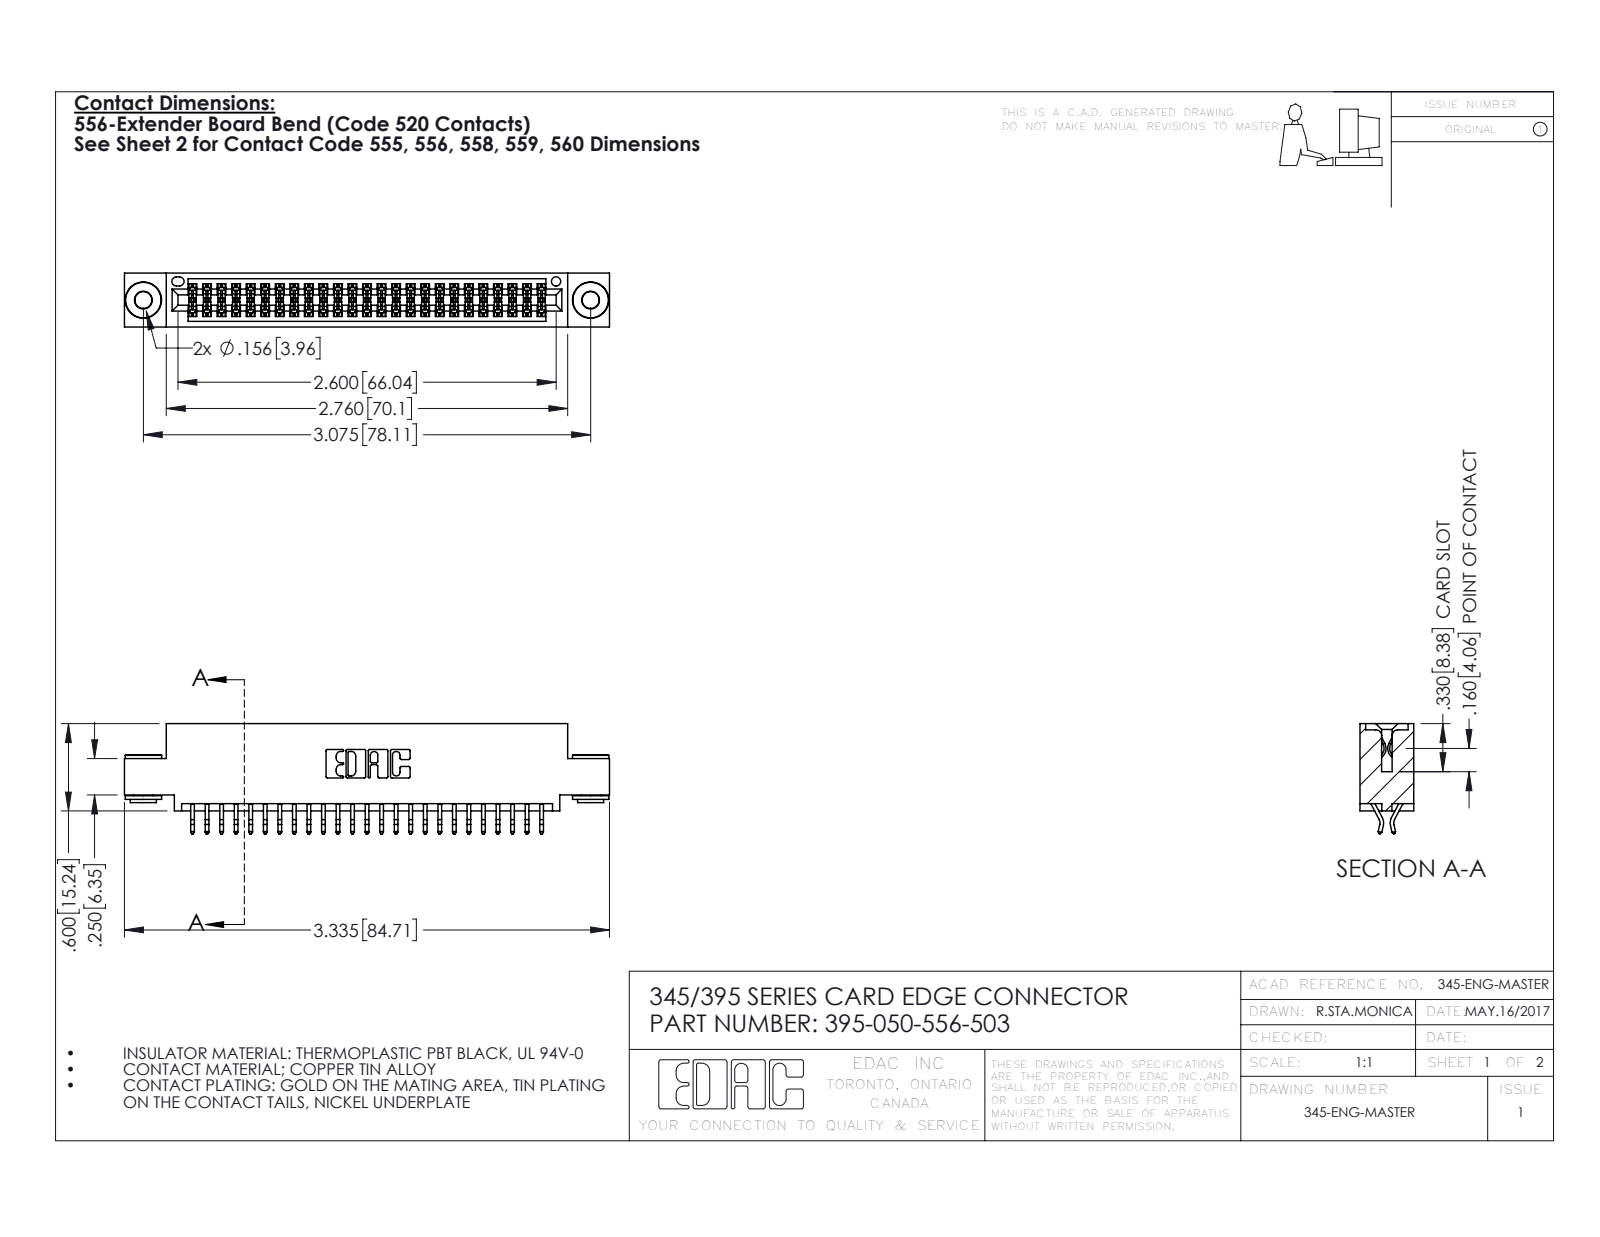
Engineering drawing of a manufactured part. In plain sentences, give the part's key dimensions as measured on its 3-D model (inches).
The part is named "395-050-556-503; 345 Part_0.110 Offset - 0.156 Dia-TH; 345-292-001_556 Tail; 345-250-002_345-250-002-102". Its 3-D file was written by "SolidWorks 2016 (CONFIG_CONTROL_DESIGN)". It is 53 solids with 2968 faces: 1944 planar, 1016 cylindrical and 8 other. Overall it measures 3.335 by 0.757 by 0.37 inches. Its volume is 0.489 cubic inches and its surface area 18.25 square inches. Round holes: 2 of diameter 0.116, 2 of diameter 0.156, 1 of diameter 0.064. Round bosses or shafts: 2 of diameter 0.25, 2 of diameter 0.18, 2 of diameter 0.136. Partial cylindrical surfaces (rounded edges, fillets, slot ends): 75 of radius 0.006, 22 of radius 0.01, 6 of radius 0.007, 6 of radius 0.031, 3 of radius 0.026, 2 of radius 0.01, 2 of radius 0.014, 2 of radius 0.019. The main face-to-face distances are 0.072, 0.298, 0.37, 0.2, 0.025, 0.098, 0.272, 0.225, 0.175, 0.149. The hole center spacings are 0.27, 2.84, 3.075.
